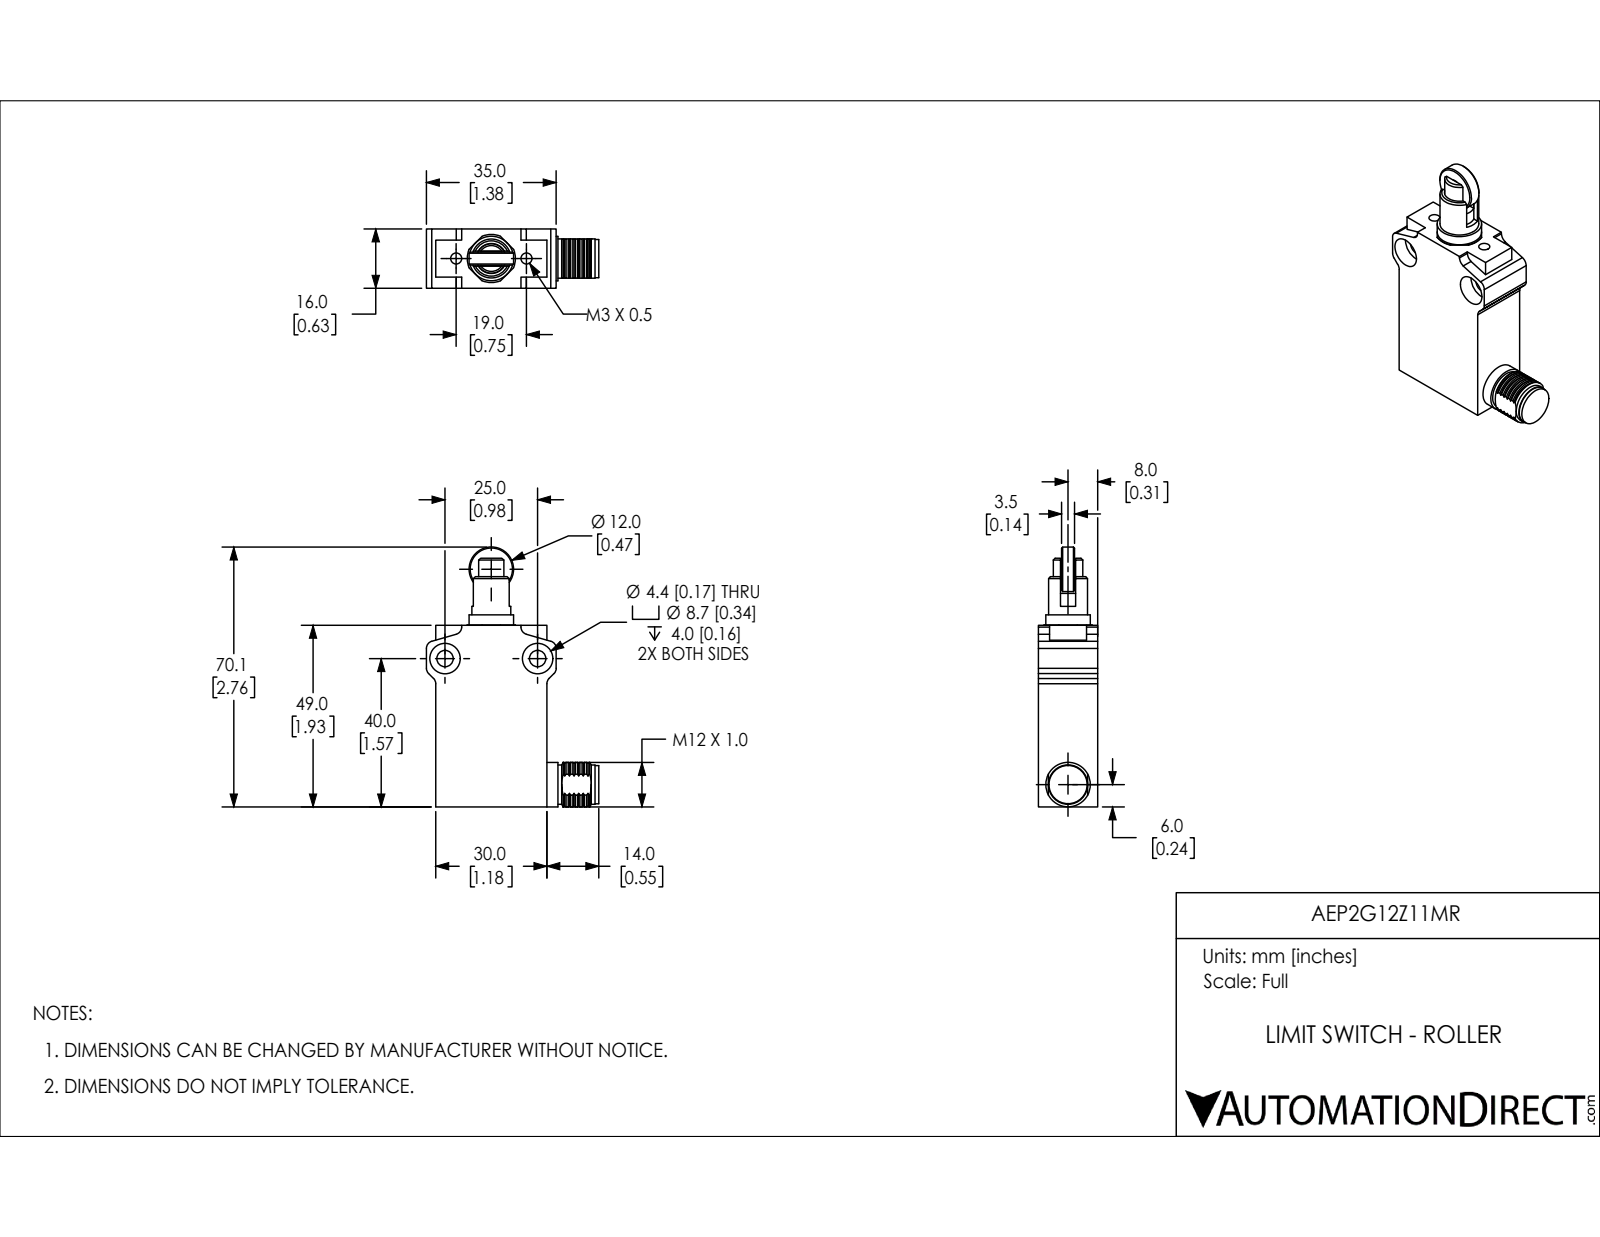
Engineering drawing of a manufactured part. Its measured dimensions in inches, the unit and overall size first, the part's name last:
Units: inches
Overall size (bounding box): 2.76 × 1.831 × 0.63
Round holes (diameter × count): ⌀0.118 ×2, ⌀0.173 ×2, ⌀0.323 ×2, ⌀0.317 ×1
Round bosses / shafts (diameter × count): ⌀0.472 ×3, ⌀0.417 ×1, ⌀0.413 ×1, ⌀0.406 ×1, ⌀0.313 ×1, ⌀0.22 ×1
Partial cylindrical surfaces — rounded edges, fillets, slot ends (radius × count): R0.079 ×8, R0.256 ×1
Main face-to-face distances: 0.63, 1.181, 1.929, 0.472, 0.234, 0.157, 0.238, 0.15, 0.396, 0.098
Hole centre spacings: 0.374, 0.748, 0.984
Bodies: 0 solids, 215 faces (68 planar, 92 cylindrical, 55 other)
Part name (STEP PRODUCT): AEP2G12Z11MR
STEP written by: SolidWorks 2018 (AUTOMOTIVE_DESIGN)
